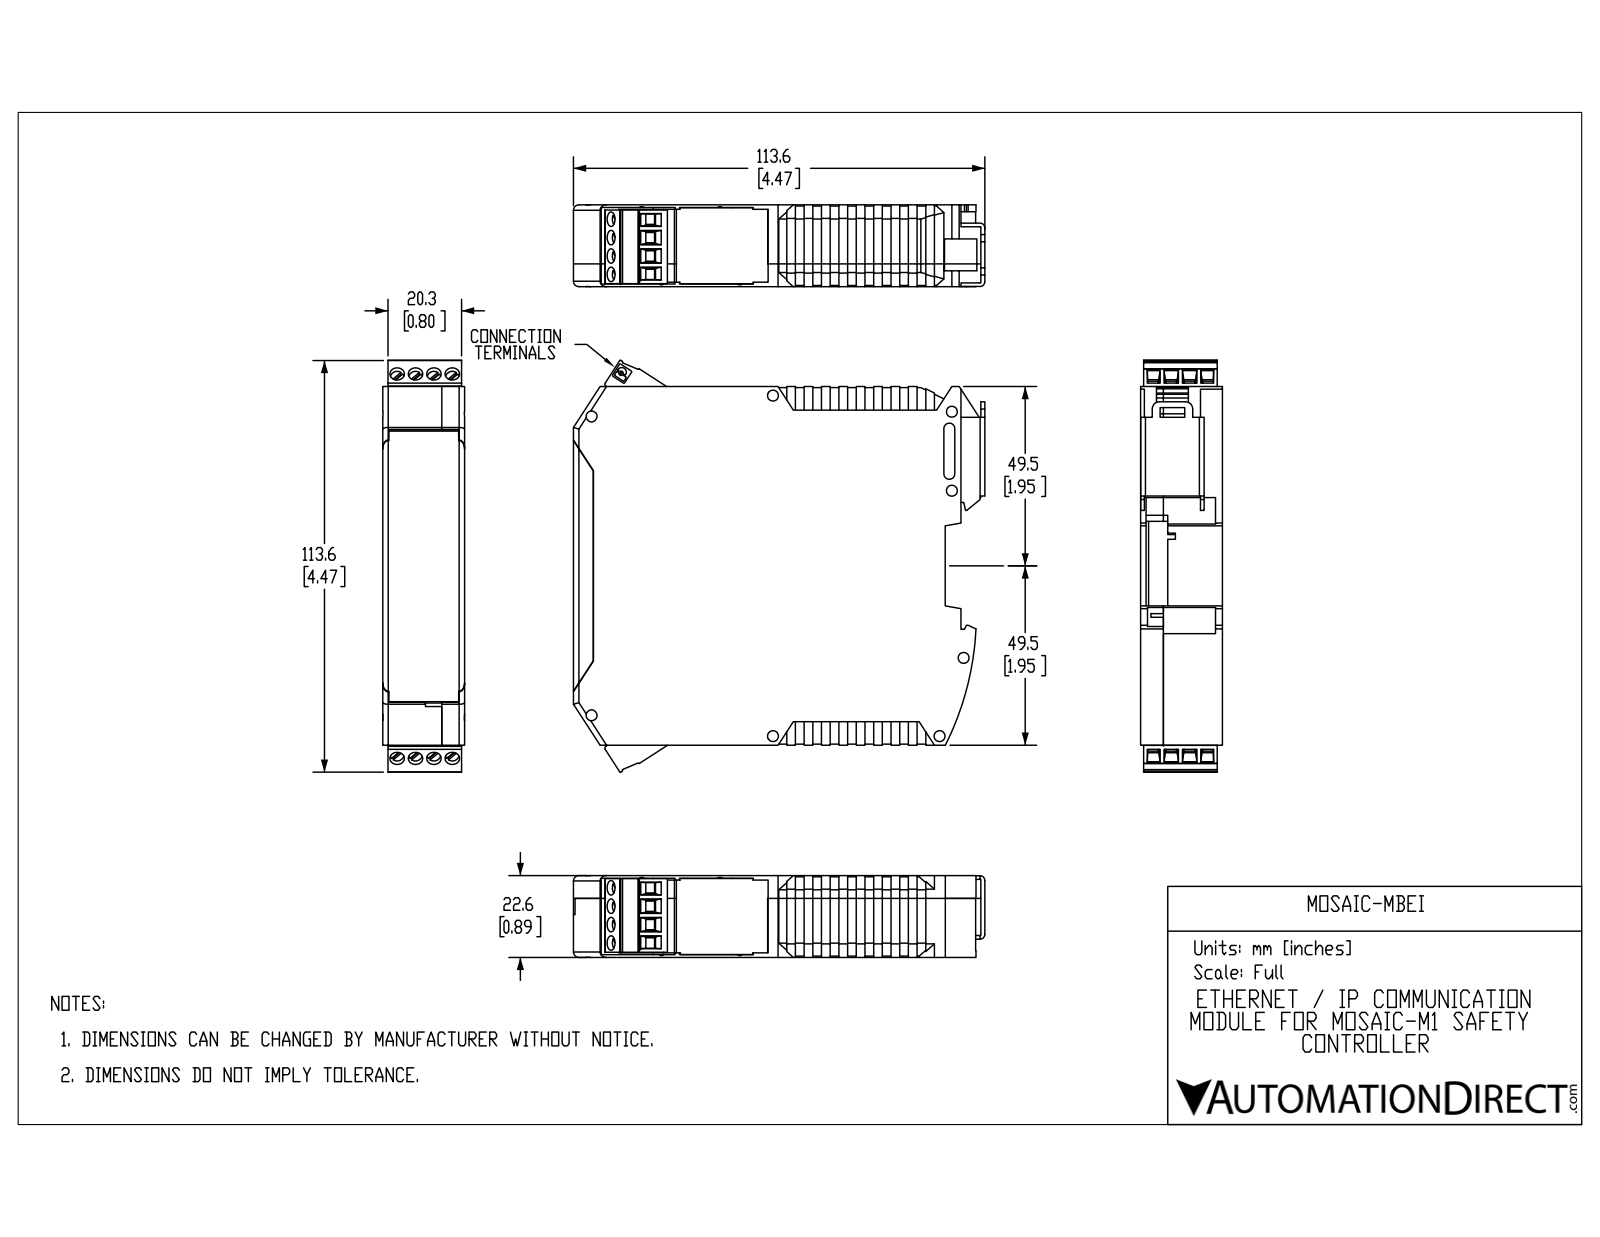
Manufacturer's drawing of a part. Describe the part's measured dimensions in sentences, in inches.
The part is named "MOSAIC-MBEI". Its 3-D file was written by "SolidWorks 2017 (AUTOMOTIVE_DESIGN)". It is 9 solids with 1361 faces: 1153 planar, 189 cylindrical and 19 other. Overall it measures 4.478 by 4.472 by 0.89 inches. Its volume is 3.595 cubic inches and its surface area 122.6 square inches. Round holes: 14 of diameter 0.118, 8 of diameter 0.157, 6 of diameter 0.055, 6 of diameter 0.11, 1 of diameter 0.063. Round bosses or shafts: 8 of diameter 0.149, 2 of diameter 0.024, 1 of diameter 0.177, 1 of diameter 0.11, 1 of diameter 0.053. Partial cylindrical surfaces (rounded edges, fillets, slot ends): 20 of radius 0.008, 10 of radius 0.03, 8 of radius 0.008, 8 of radius 0.011, 8 of radius 0.028, 8 of radius 0.059, 8 of radius 0.115, 7 of radius 0.012. The main face-to-face distances are 0.049, 0.841, 0.89, 0.791, 0.062, 0.062, 0.039, 2.67, 2.732, 2.608. The hole center spacings are 0.2, 0.4, 0.2, 0.246, 0.287, 0.4, 0.575, 0.6.
